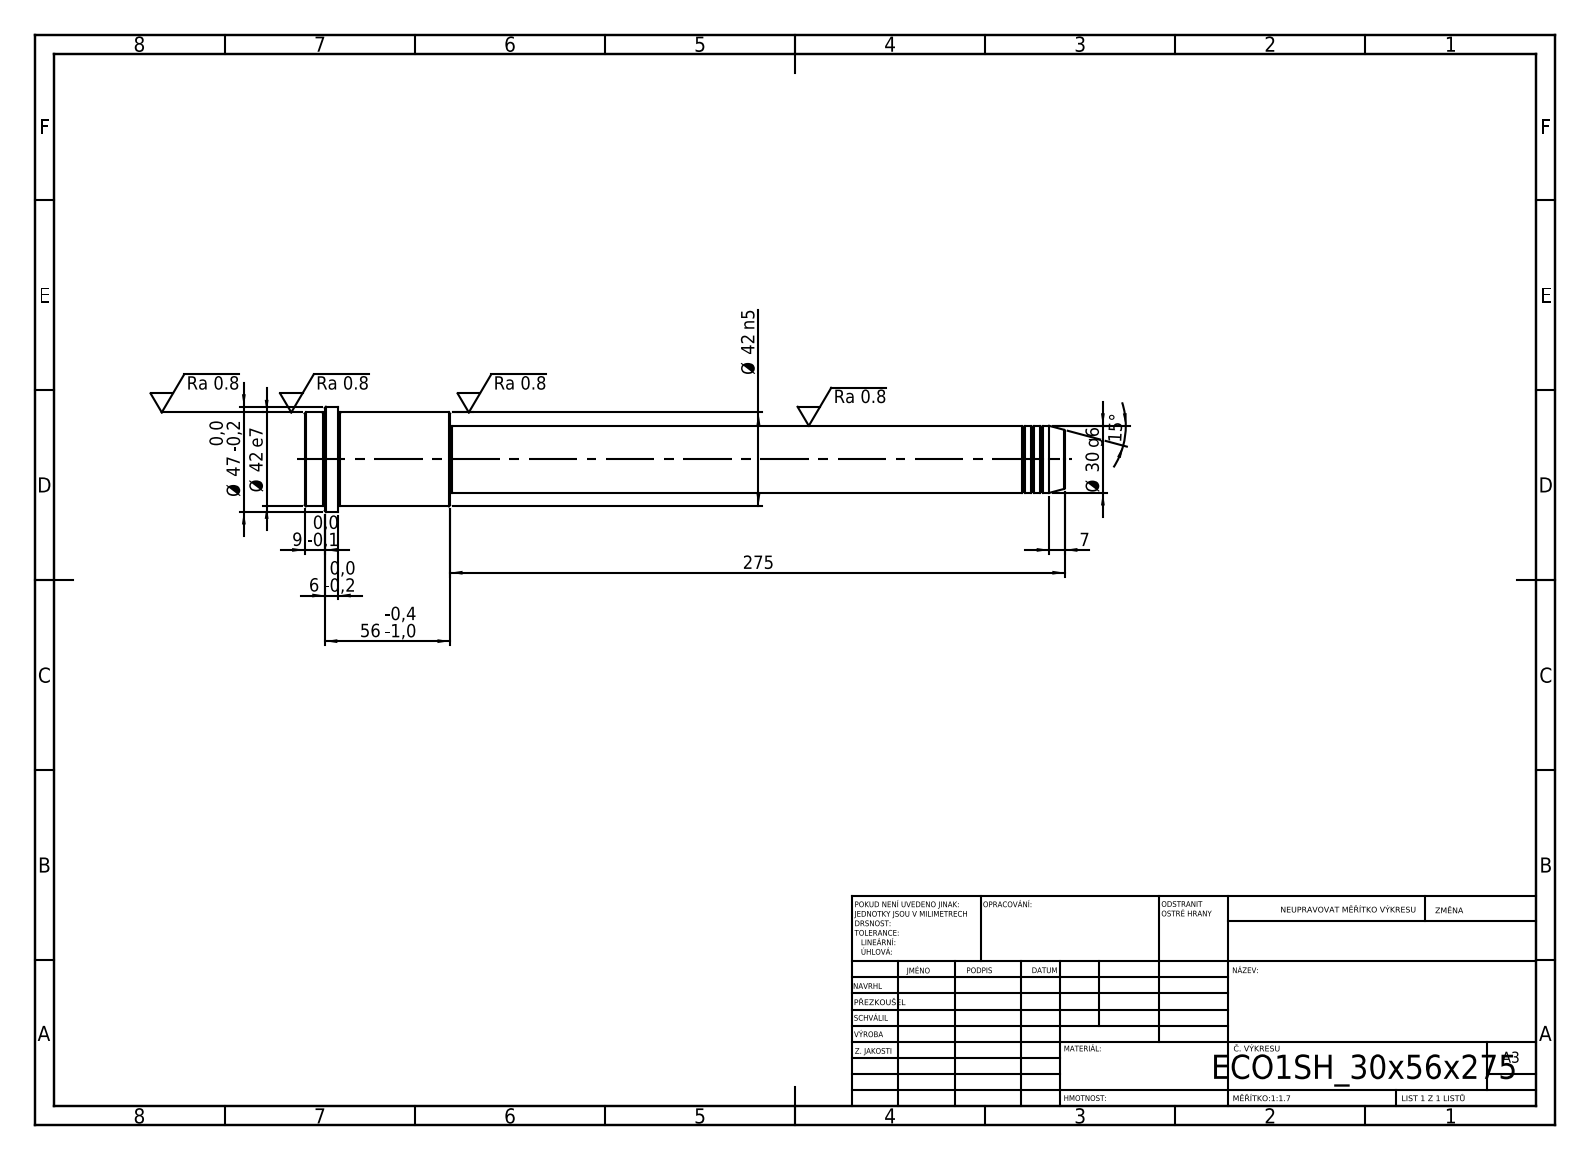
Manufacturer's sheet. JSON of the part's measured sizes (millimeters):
{"step_written_by": "SolidWorks 2019 (CONFIG_CONTROL_DESIGN)", "units": "millimeters", "bodies": {"solids": 1, "faces": 52, "planar": 6, "cylindrical": 16, "other": 30}, "overall_size": [340, 47, 47], "volume_mm3": 285632, "surface_area_mm2": 38129, "round_bosses_or_shafts": [[47, 1], [42, 1], [30, 1], [29, 1]], "face_to_face_distances": [65, 275, 340, 325, 50, 15, 331, 56, 6, 9]}
